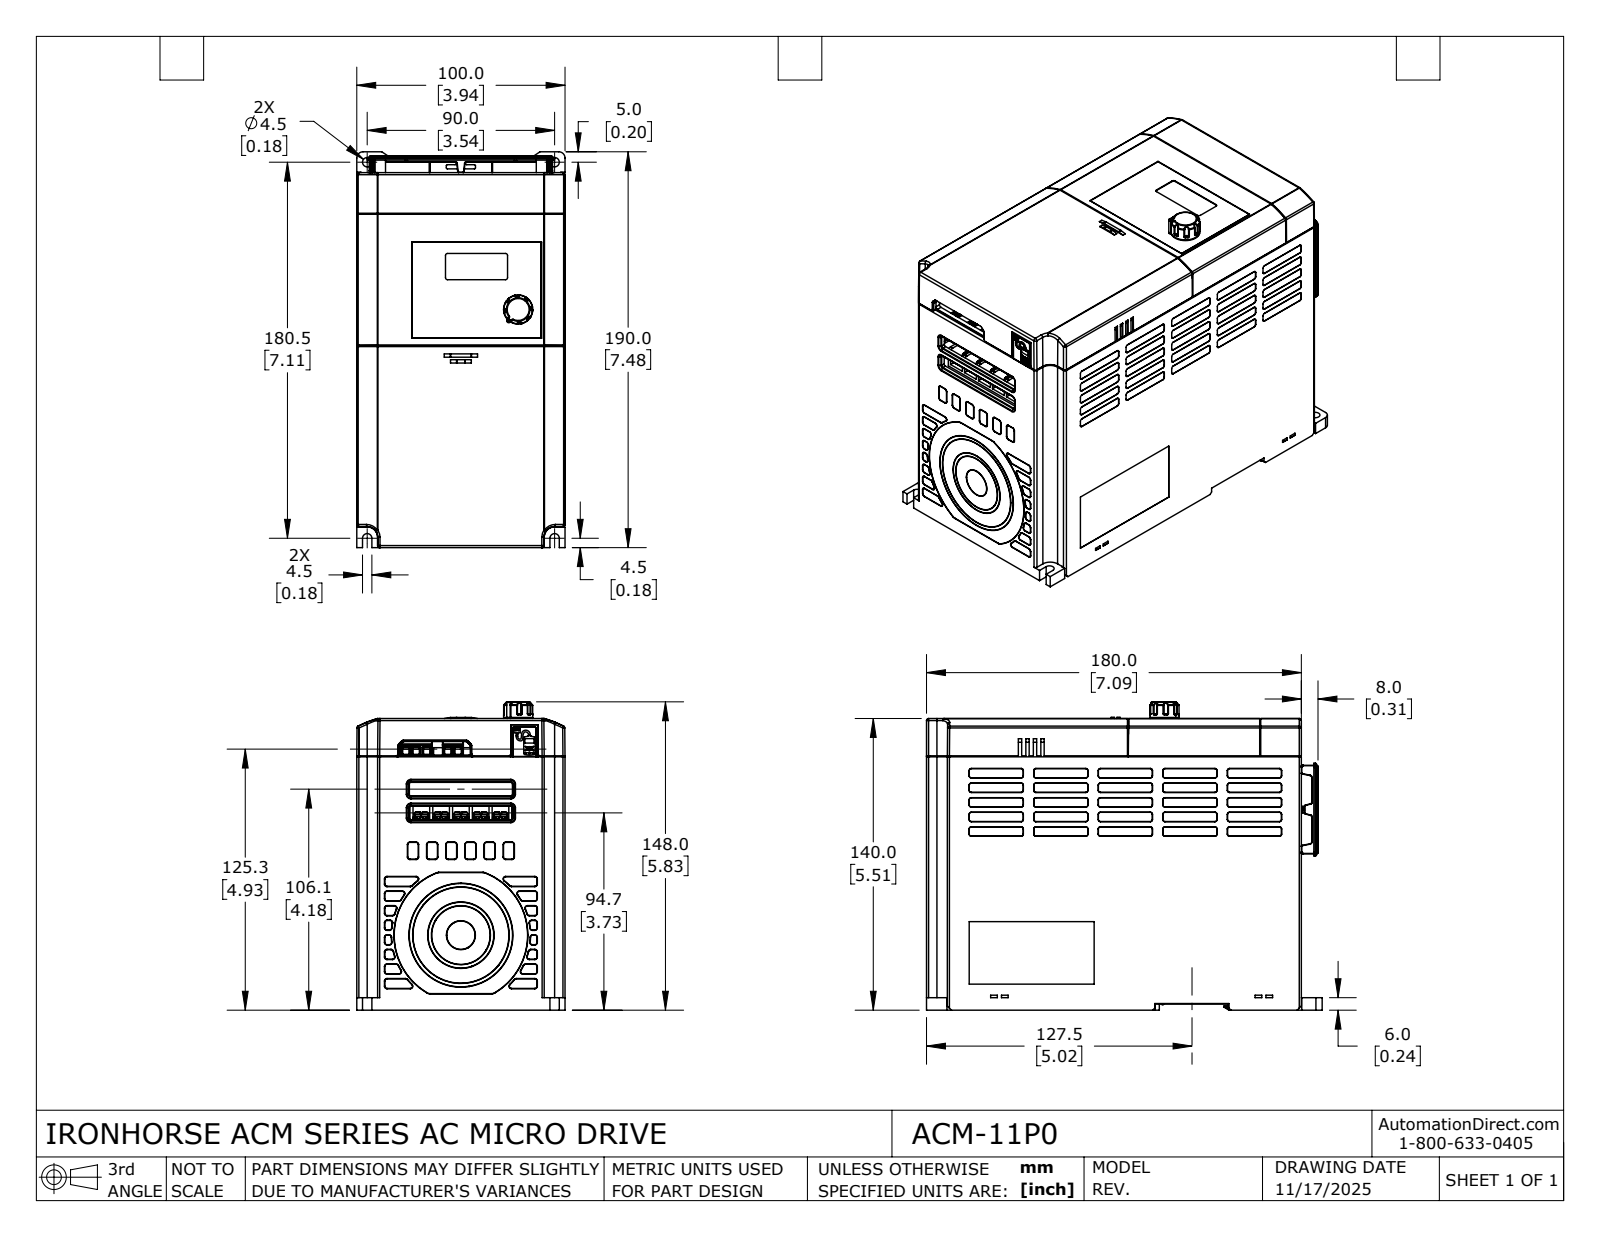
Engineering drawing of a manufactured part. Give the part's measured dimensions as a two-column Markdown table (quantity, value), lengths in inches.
| quantity | value |
| --- | --- |
| part name | ACM-11P0 |
| STEP written by | SolidWorks 2024 (AUTOMOTIVE_DESIGN) |
| units | inches |
| bodies | 6 solids, 5553 faces (2779 planar, 1549 cylindrical, 1225 other) |
| overall size | 7.48 × 5.827 × 3.937 |
| volume | 22.39 in³ |
| surface area | 396.6 in² |
| round holes (diameter × count) | 0.409 × 6, 0.118 × 2, 0.157 × 2, 0.177 × 2, 0.315 × 2, 0.449 × 2, 0.039 × 1, 0.394 × 1, 0.472 × 1 |
| round bosses / shafts (diameter × count) | 0.472 × 7, 0.512 × 2, 0.256 × 2, 0.236 × 2, 0.551 × 1, 0.543 × 1, 0.032 × 1 |
| partial cylindrical surfaces (radius × count) | 0.008 × 641, 0.02 × 142, 0.039 × 94, 0.012 × 22, 0.031 × 16, 0.079 × 10, 0.059 × 8, 0.005 × 6 |
| main face-to-face distances | 3.61, 0.02, 0.139, 3.748, 0.189, 3.937, 3.798, 5.276, 5.256, 0.236 |
| hole center spacings | 0.874, 0.384, 0.921, 1.213, 1.26, 1.728, 1.748, 2.063 |
